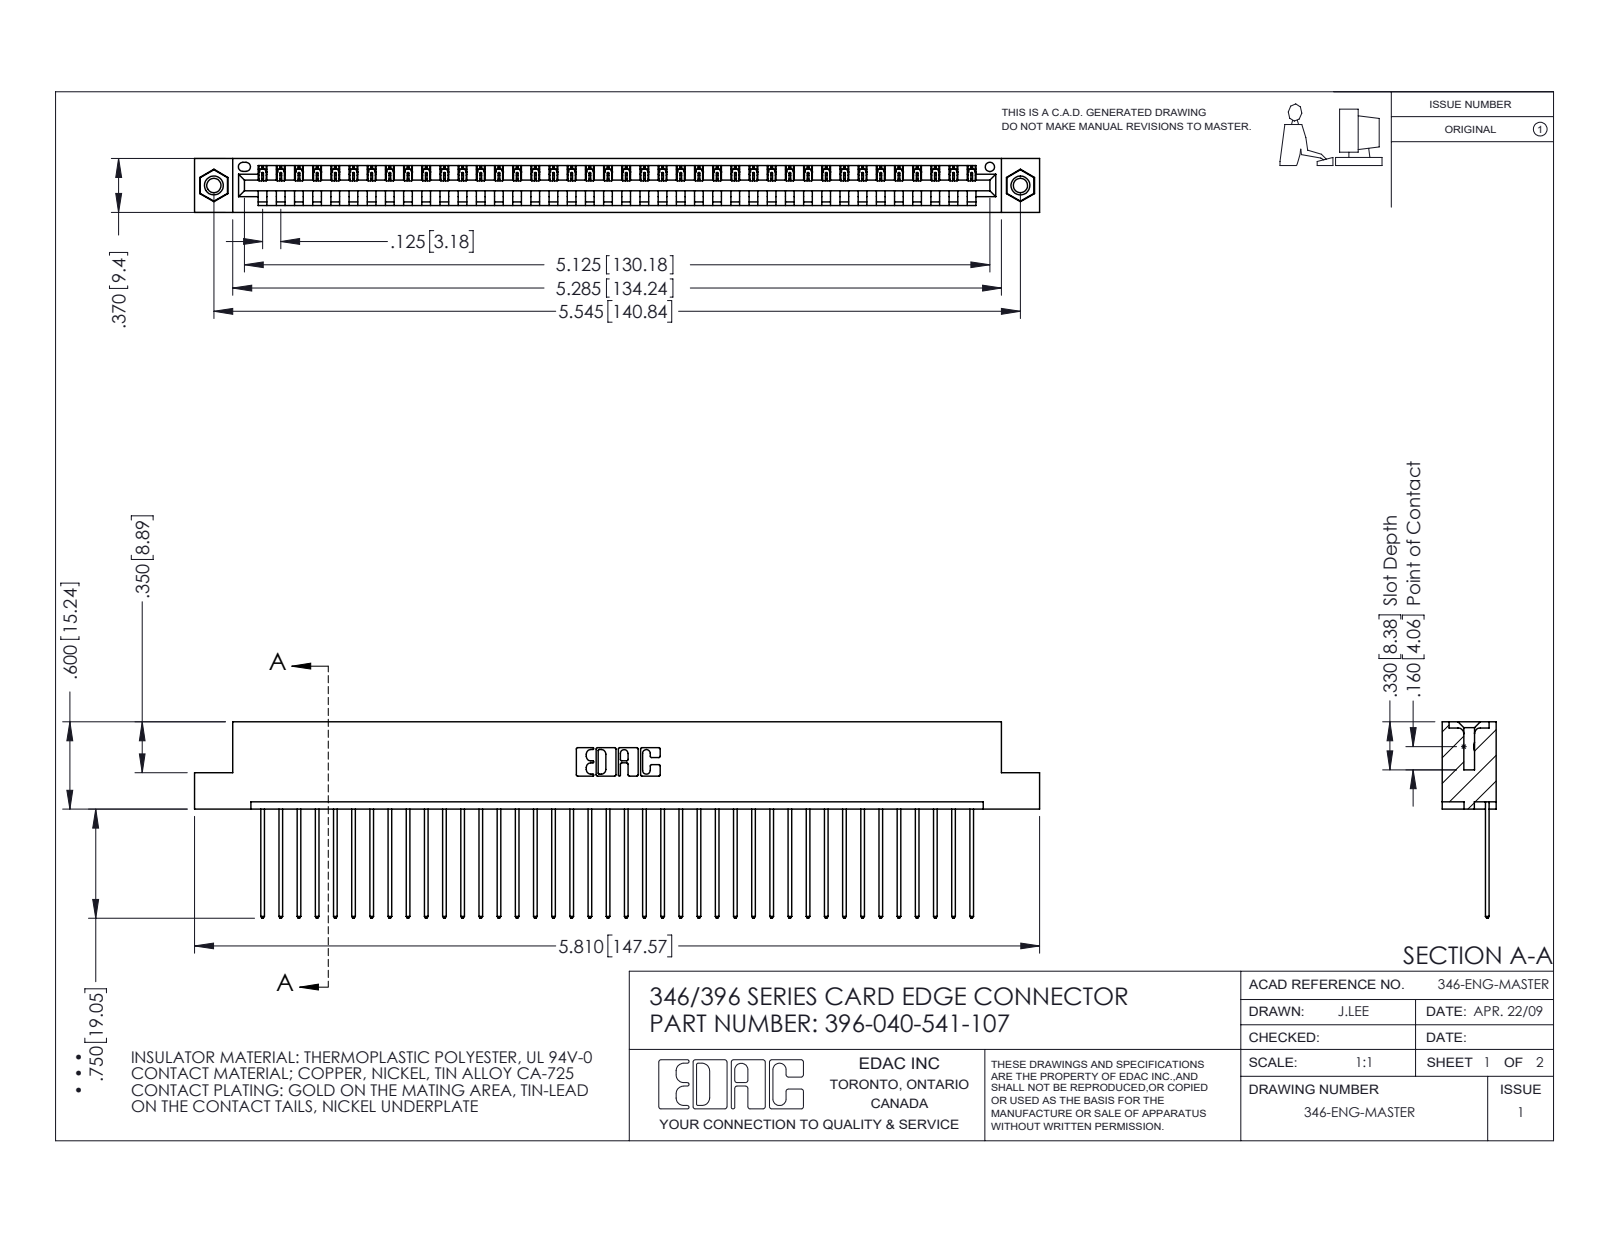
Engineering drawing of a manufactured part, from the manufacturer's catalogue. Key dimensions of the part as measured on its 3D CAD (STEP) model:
Part name (STEP PRODUCT): 345-250-001_345-250-005-103; 396-040-541-107; 345-292-001_345-293-141; 346 Part_Flush Mounting Lugs - 0.156 Dia-TI
STEP written by: SolidWorks 2016 (CONFIG_CONTROL_DESIGN)
Units: inches
Bodies: 43 solids, 2502 faces (1708 planar, 778 cylindrical, 16 other)
Overall size (bounding box): 5.81 × 1.35 × 0.37
Volume: 0.868 in³ · Surface area: 28.81 in²
Round holes (diameter × count): ⌀0.098 ×2, ⌀0.125 ×2, ⌀0.156 ×2, ⌀0.064 ×1
Round bosses / shafts (diameter × count): ⌀0.155 ×2
Partial cylindrical surfaces — rounded edges, fillets, slot ends (radius × count): R0.006 ×80, R0.01 ×80, R0.01 ×22, R0.007 ×6, R0.031 ×6, R0.026 ×3, R0.031 ×2, R0.04 ×2
Main face-to-face distances: 0.048, 0.322, 0.37, 0.25, 0.072, 0.298, 0.025, 0.148, 0.222, 0.1
Hole centre spacings: 0.246, 5.336, 5.545
